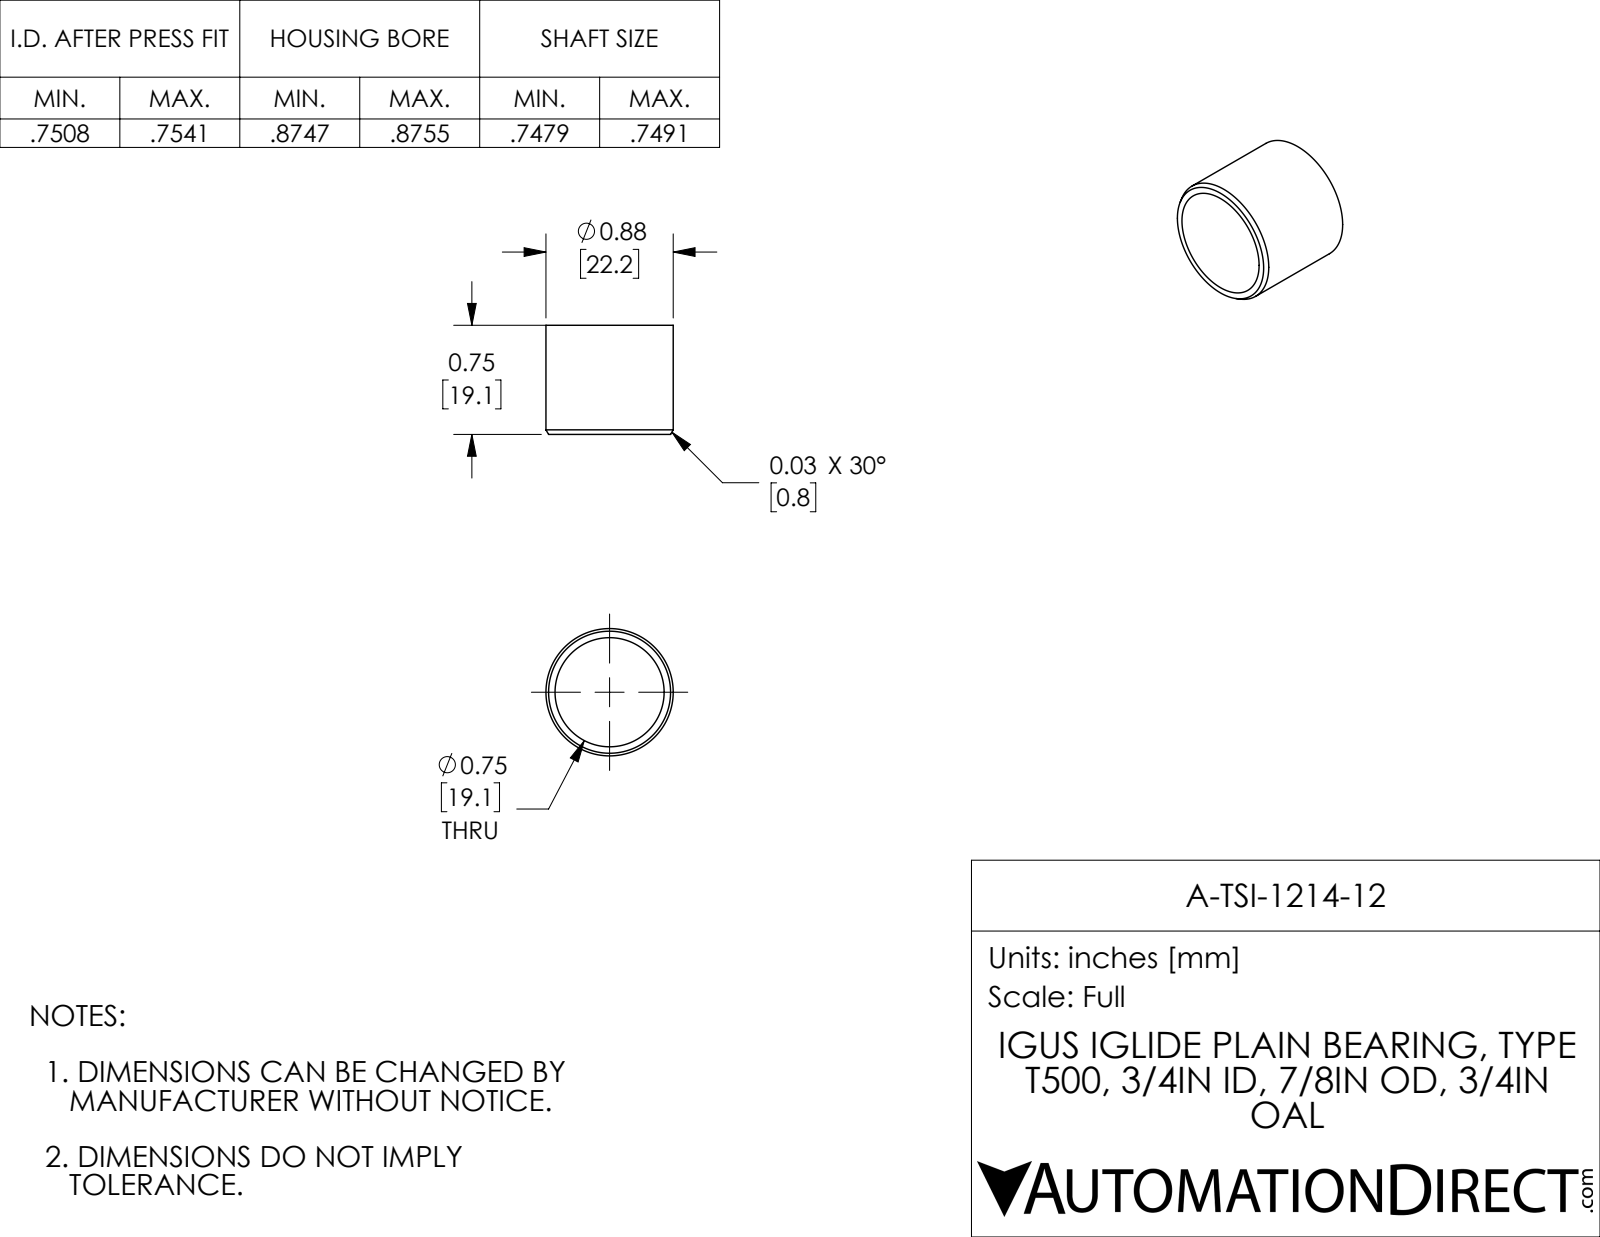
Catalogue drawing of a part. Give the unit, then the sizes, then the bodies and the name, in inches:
Units: inches
Overall size (bounding box): 0.875 × 0.875 × 0.75
Round holes (diameter × count): ⌀0.75 ×1
Round bosses / shafts (diameter × count): ⌀0.875 ×1
Main face-to-face distances: 0.75
Volume: 0.119 in³ · Surface area: 4.091 in²
Bodies: 1 solid, 10 faces (2 planar, 4 cylindrical, 4 other)
Part name (STEP PRODUCT): A-TSI-1214-12
STEP written by: SolidWorks 2017 (AUTOMOTIVE_DESIGN)
